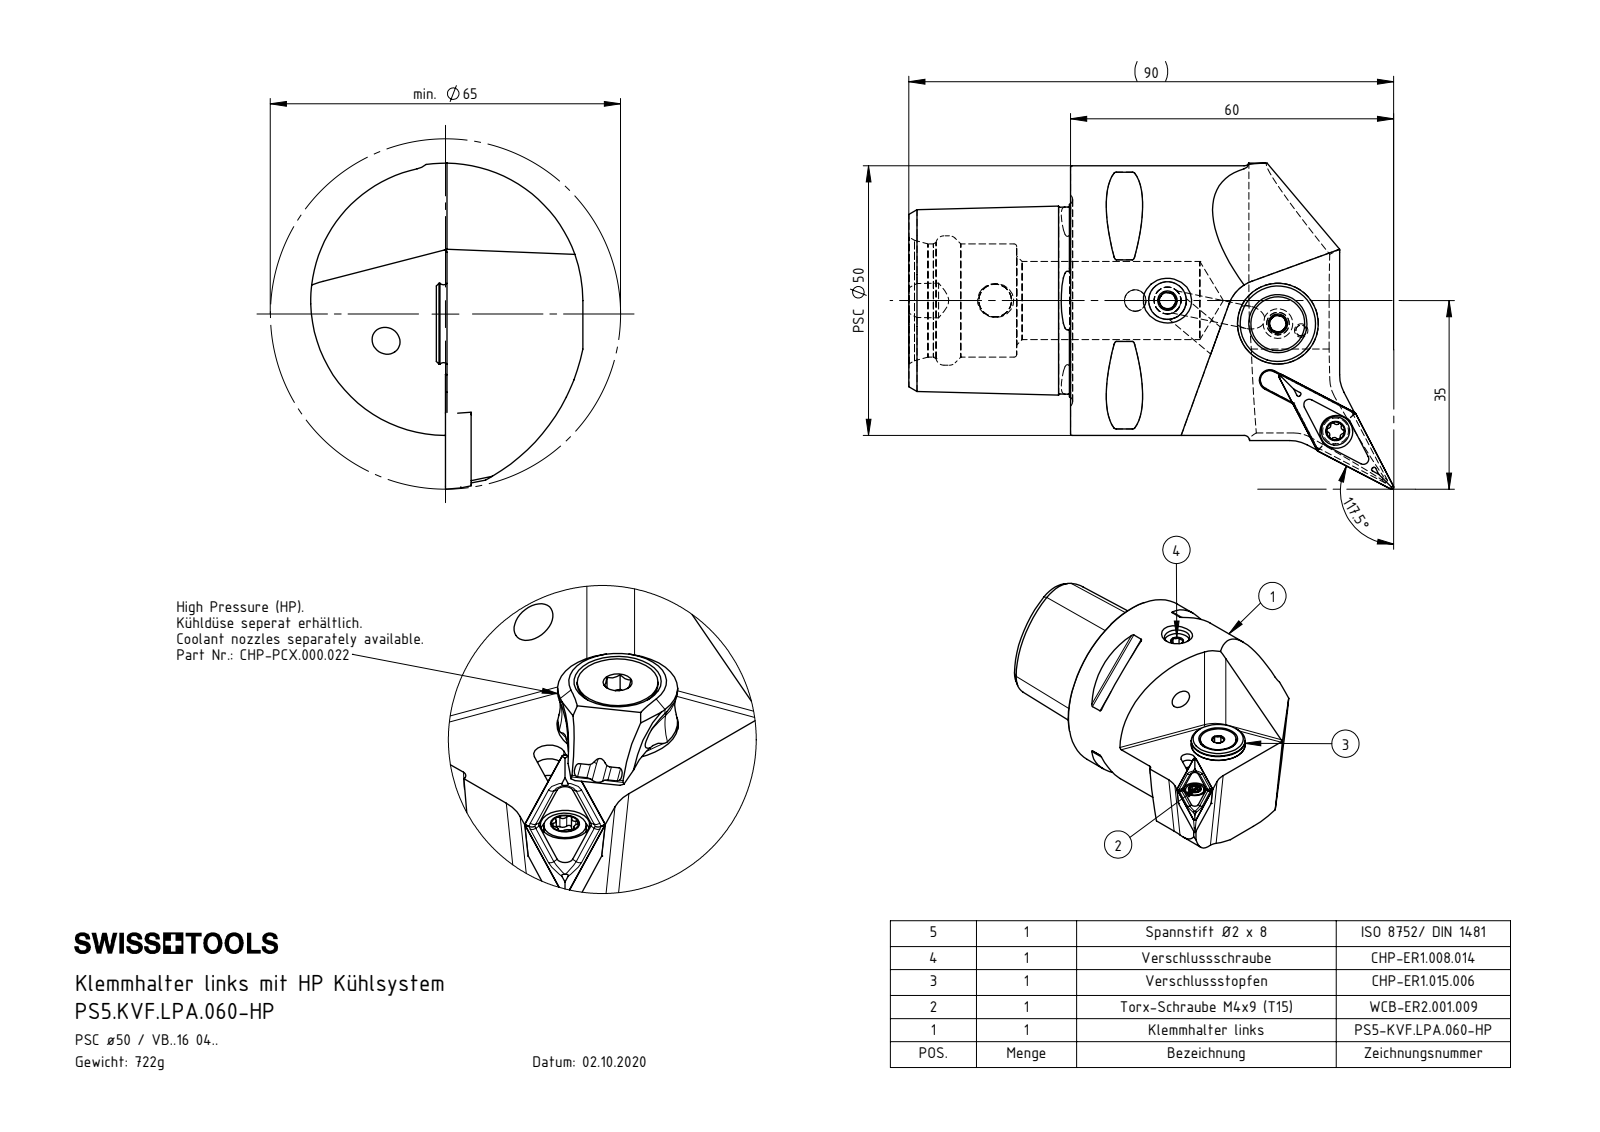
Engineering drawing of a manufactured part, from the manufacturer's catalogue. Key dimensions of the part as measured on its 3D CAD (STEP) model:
Part name (STEP PRODUCT): PS5.KVF.LPA.060-HP; VBMT160404; WCB-ER2.001.009_A; CHP-PCX.000.022_Dse (+7 more)
STEP written by: SolidWorks 2017 (AUTOMOTIVE_DESIGN)
Units: millimetres
Bodies: 9 solids, 487 faces (108 planar, 137 cylindrical, 242 other)
Overall size (bounding box): 90 × 60.5 × 50.5
Volume: 91 961 mm³ · Surface area: 22 682 mm²
Round holes (diameter × count): ⌀4.2 ×2, ⌀5 ×2, ⌀6.1 ×2, ⌀1.2 ×1, ⌀2 ×1, ⌀3 ×1, ⌀3.3 ×1, ⌀4 ×1, ⌀4.4 ×1, ⌀5.3 ×1, ⌀7 ×1, ⌀13 ×1
Round bosses / shafts (diameter × count): ⌀50 ×1, ⌀14.85 ×1, ⌀13.4 ×1, ⌀10 ×1, ⌀8 ×1, ⌀5.5 ×1, ⌀5.25 ×1, ⌀5 ×1
Partial cylindrical surfaces — rounded edges, fillets, slot ends (radius × count): R0.5 ×12, R1 ×7, R0.34 ×6, R0.59 ×6, R6 ×3, R7 ×3, R0.15 ×2, R1.1 ×2
Main face-to-face distances: 30, 4.46, 19.18, 4.5, 44.4, 20.7, 20.74, 25.2, 1.5, 3
Hole centre spacings: 4.5, 6, 19.73, 19.92, 20.93, 22.6, 22.81, 25.43
